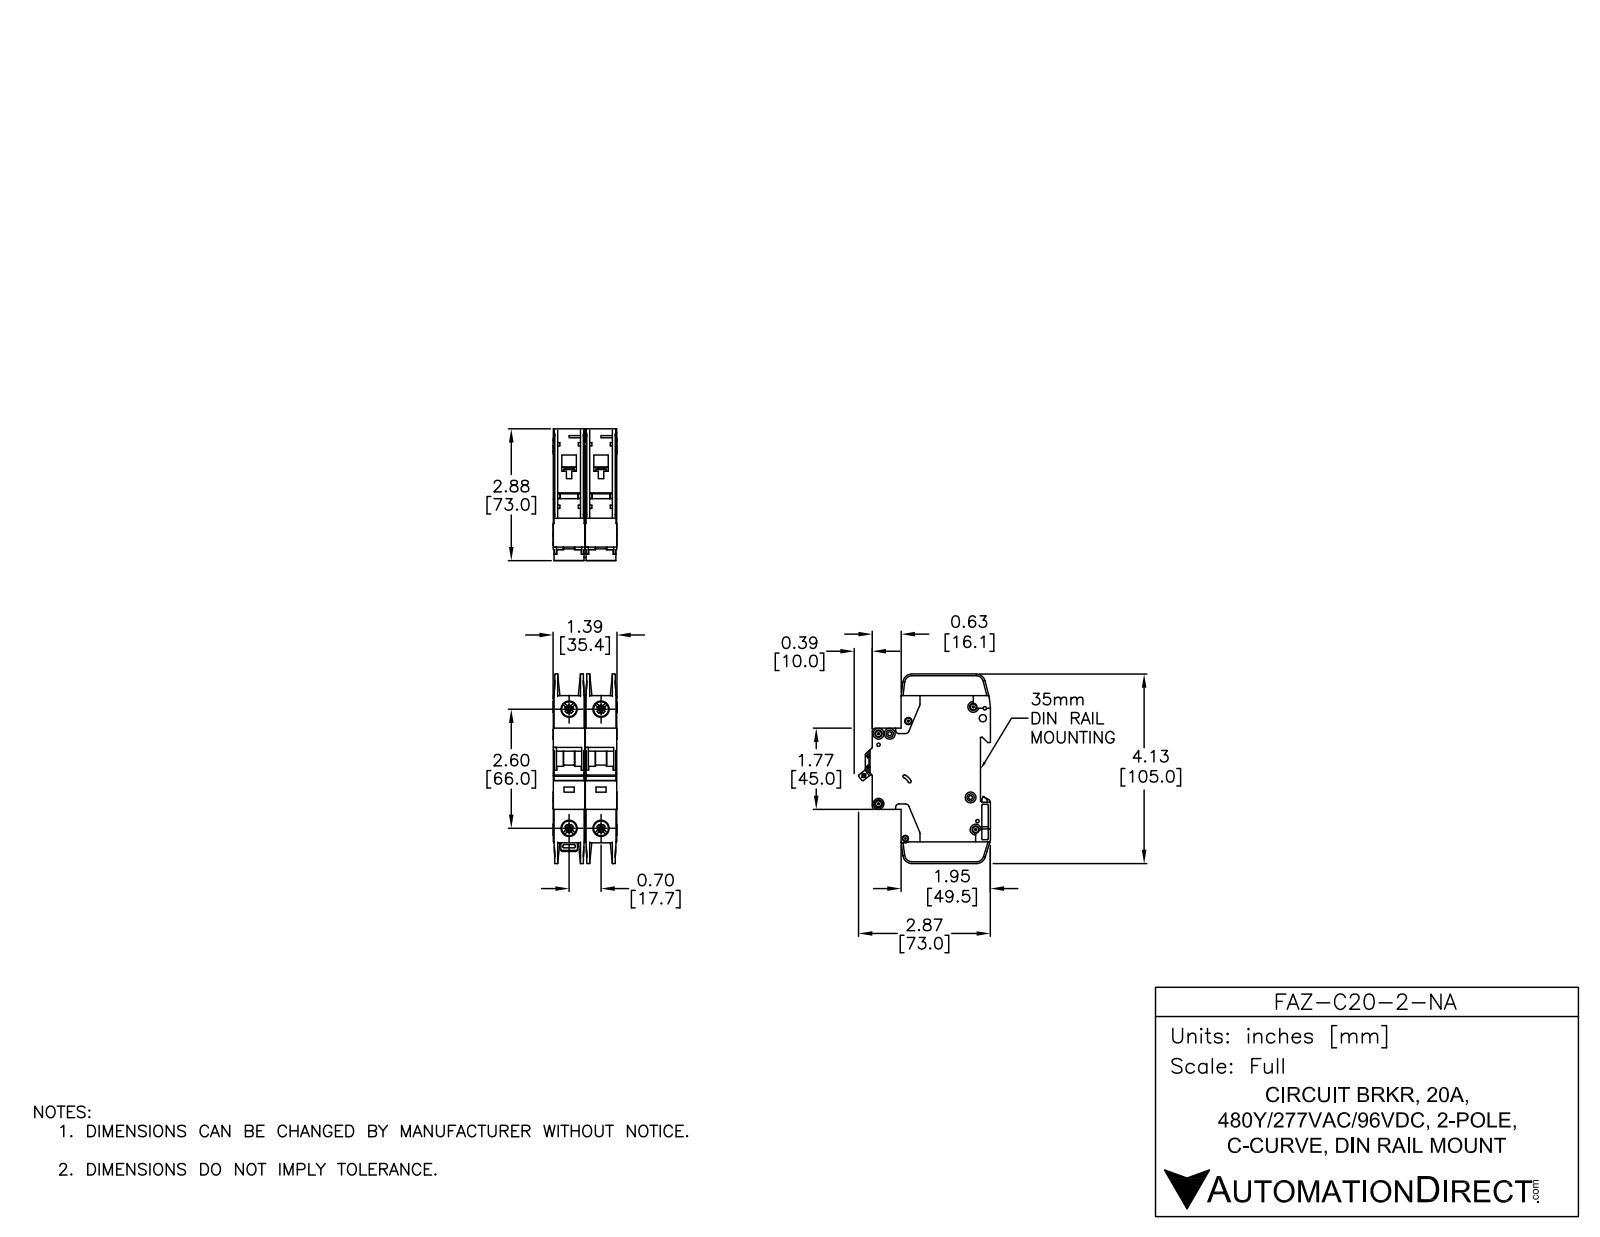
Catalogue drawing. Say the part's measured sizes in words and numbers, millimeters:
The part is named "FAZ-C20-2-NA". Its 3-D file was written by "SolidWorks 2014 (AUTOMOTIVE_DESIGN)". It is 6 solids with 1568 faces: 818 planar, 526 cylindrical and 224 other. Overall it measures 105 by 73.04 by 35.4 millimeters. Its volume is 155 390 cubic millimeters and its surface area 49 479 square millimeters. Round holes: 7 of diameter 3.6, 4 of diameter 7.15, 4 of diameter 8.2, 2 of diameter 1.09, 2 of diameter 1.5, 2 of diameter 4, 1 of diameter 1.9, 1 of diameter 2.15, 1 of diameter 2.2, 1 of diameter 2.55, 1 of diameter 3.3, 1 of diameter 3.4. Round bosses or shafts: 7 of diameter 6, 2 of diameter 2.5. Partial cylindrical surfaces (rounded edges, fillets, slot ends): 47 of radius 0.25, 24 of radius 0.5, 18 of radius 1, 12 of radius 2, 5 of radius 5, 4 of radius 1.8, 4 of radius 4, 2 of radius 0.2. The main face-to-face distances are 17.7, 17.5, 0.7, 15.05, 2.45, 1.75, 15.75, 13.3, 35.2, 17. The hole center spacings are 6.2, 17.7, 66, 68.33, 5.19, 6.1, 8.19, 8.56.
